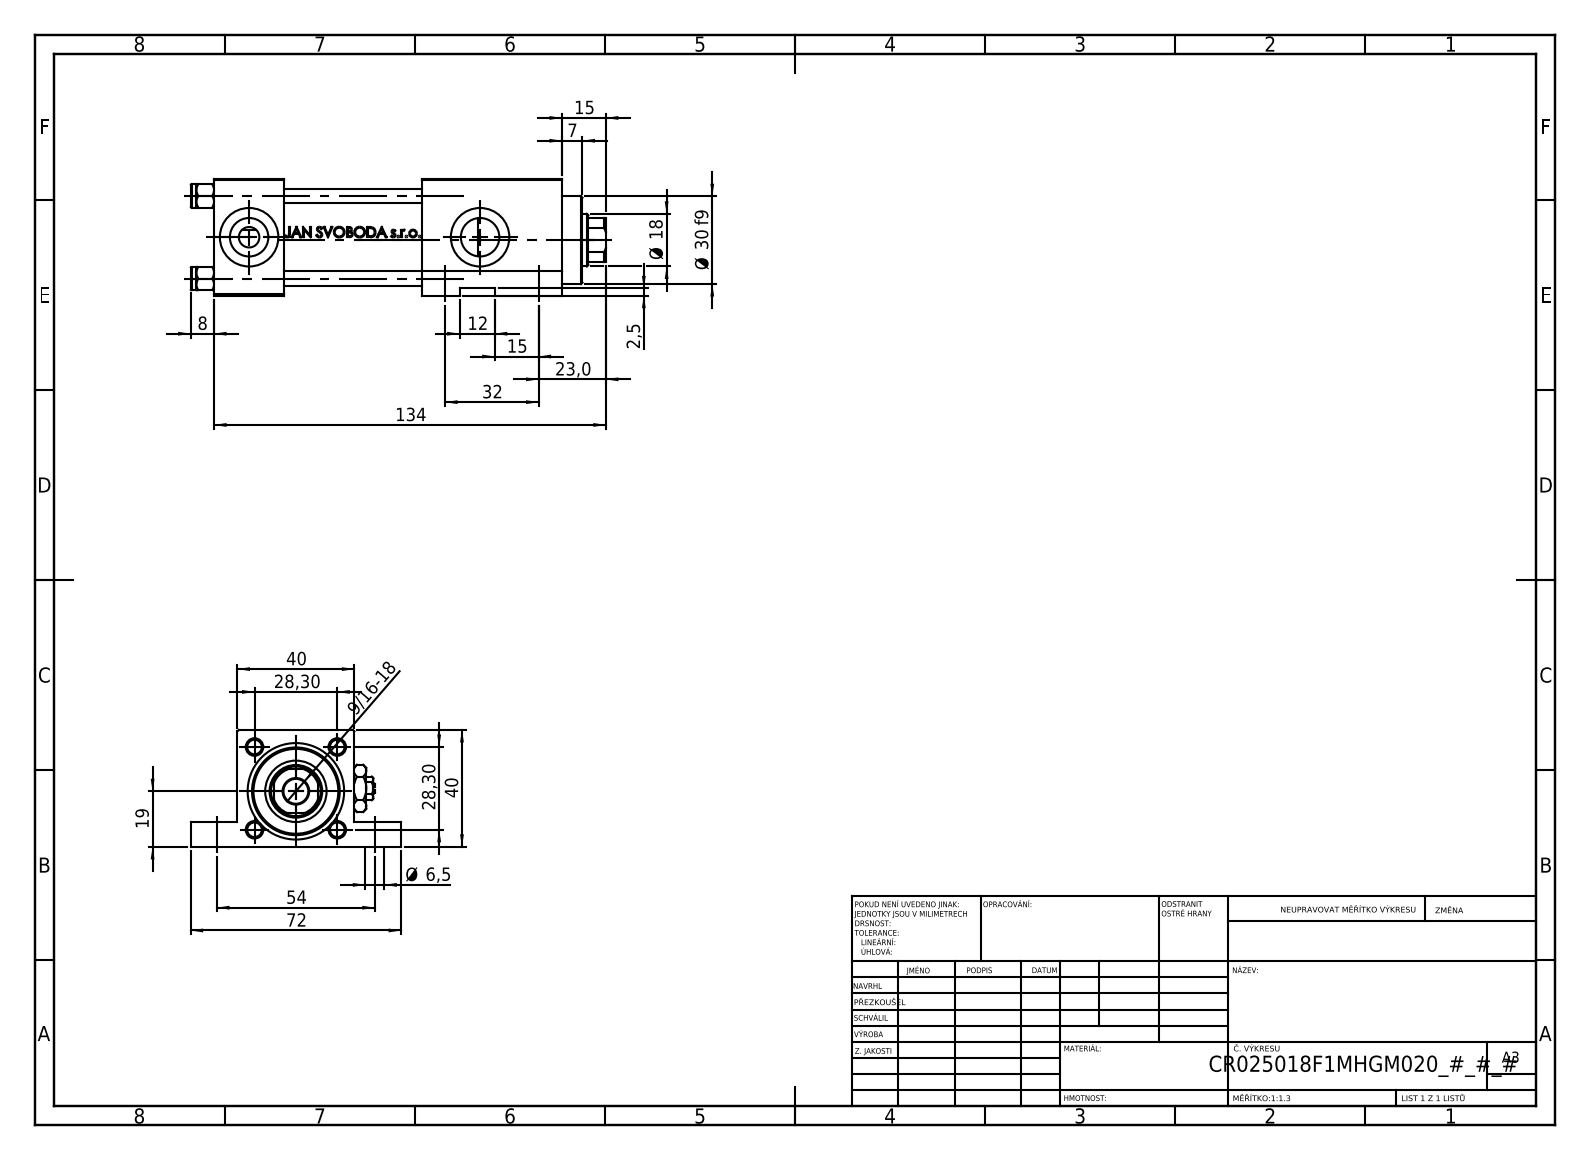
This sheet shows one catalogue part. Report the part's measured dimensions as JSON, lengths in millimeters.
{"part_name": "Zatka_pro_OIL_PORT; V215CR_F_TYCINKA; NUT_M5_F; V215CR_VCP_F (+2 more)", "step_written_by": "SolidWorks 2019 (CONFIG_CONTROL_DESIGN)", "units": "millimeters", "bodies": {"solids": 12, "faces": 1147, "planar": 459, "cylindrical": 128, "other": 560}, "overall_size": [142, 72, 40], "volume_mm3": 159470, "surface_area_mm2": 61464, "round_holes": [[5, 4], [6.5, 4], [20, 4], [13.16, 3], [7, 2], [8.5, 1], [18, 1], [21, 1], [25, 1], [30, 1]], "round_bosses_or_shafts": [[8, 4], [31, 1]], "partial_cylinders_radius": [[8.5, 1]], "face_to_face_distances": [40, 24, 8.5, 31.5, 47, 71, 6, 48, 119, 95], "hole_center_spacings": [28.3, 19.32, 20.73, 32, 40.02, 54, 62.77, 7]}
